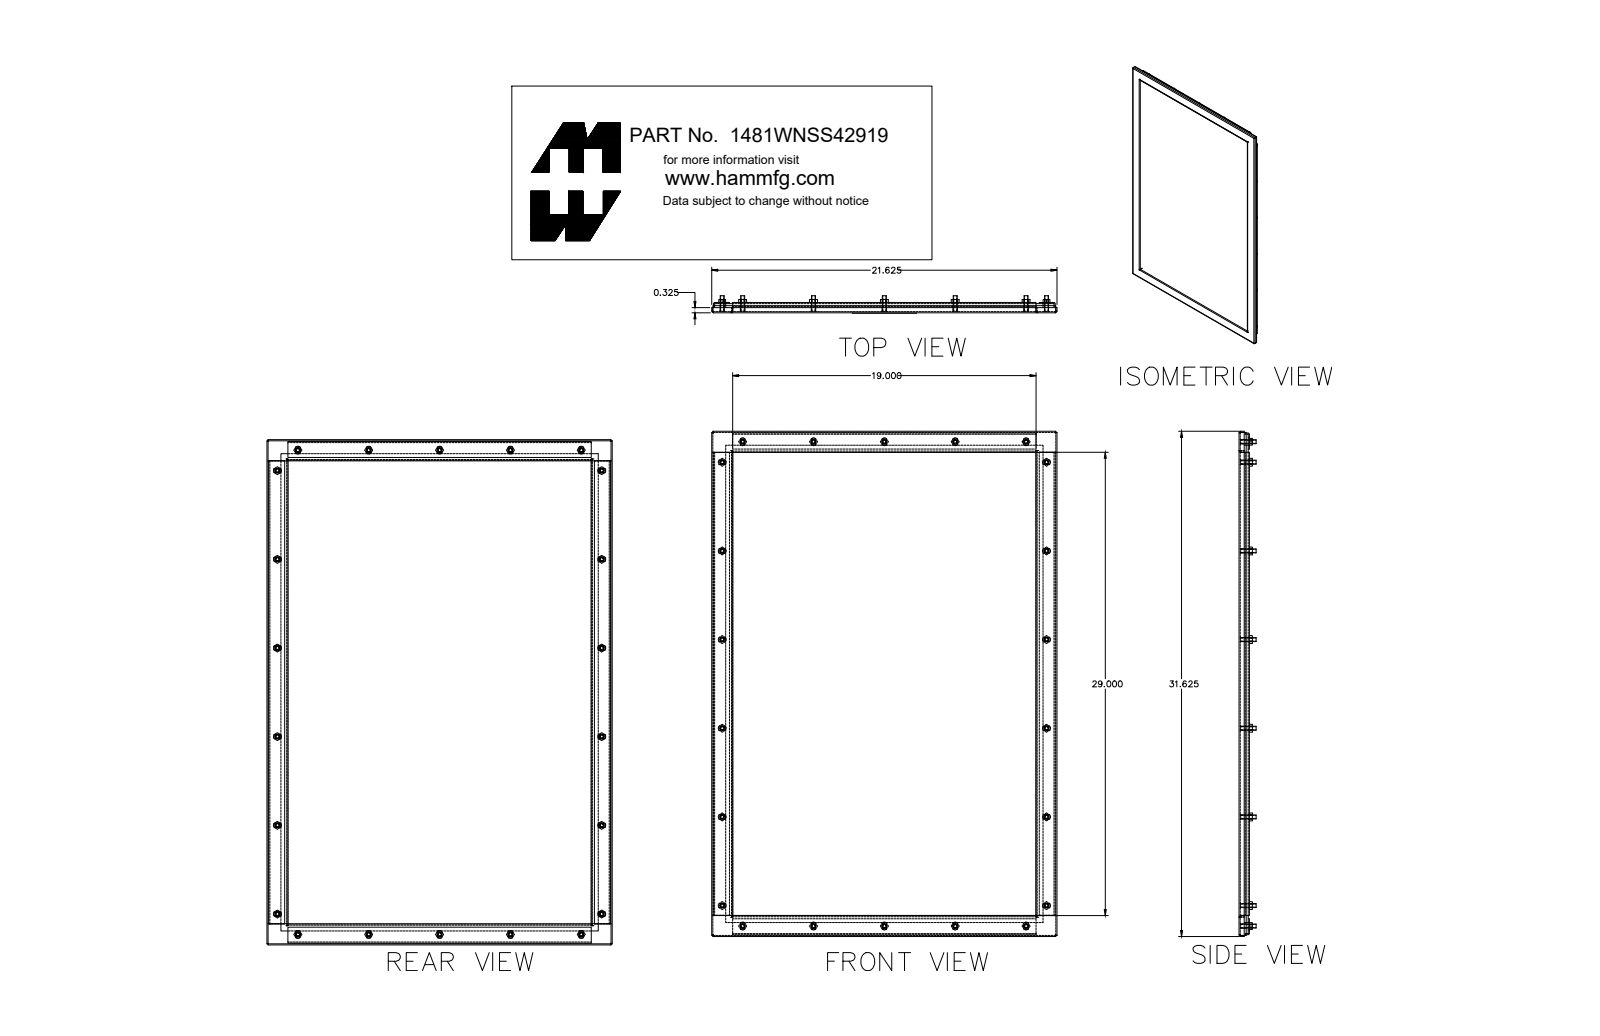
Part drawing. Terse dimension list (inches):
name: 1481WN4SS2919_Default
written by: SolidWorks 2019 (CONFIG_CONTROL_DESIGN)
unit: in
bodies: 51 solids, 564 faces (356 planar, 200 cylindrical, 8 other)
size: 32.025 × 22.025 × 1.072
volume: 183.2 in³; area: 2 215 in²
holes: 22× ⌀0.196, 22× ⌀0.328
bosses: 22× ⌀0.313, 22× ⌀0.25
rounds: 8× R0.036, 8× R0.108, 4× R0.016, 4× R0.088
face distances: 0.25, 0.072, 0.253, 0.503, 0.325, 0.575, 0.575, 0.647, 0.322, 0.072
hole spacings: 30.636, 30.313, 31.585, 4.437, 5.55, 21.057, 33.107, 11.1
